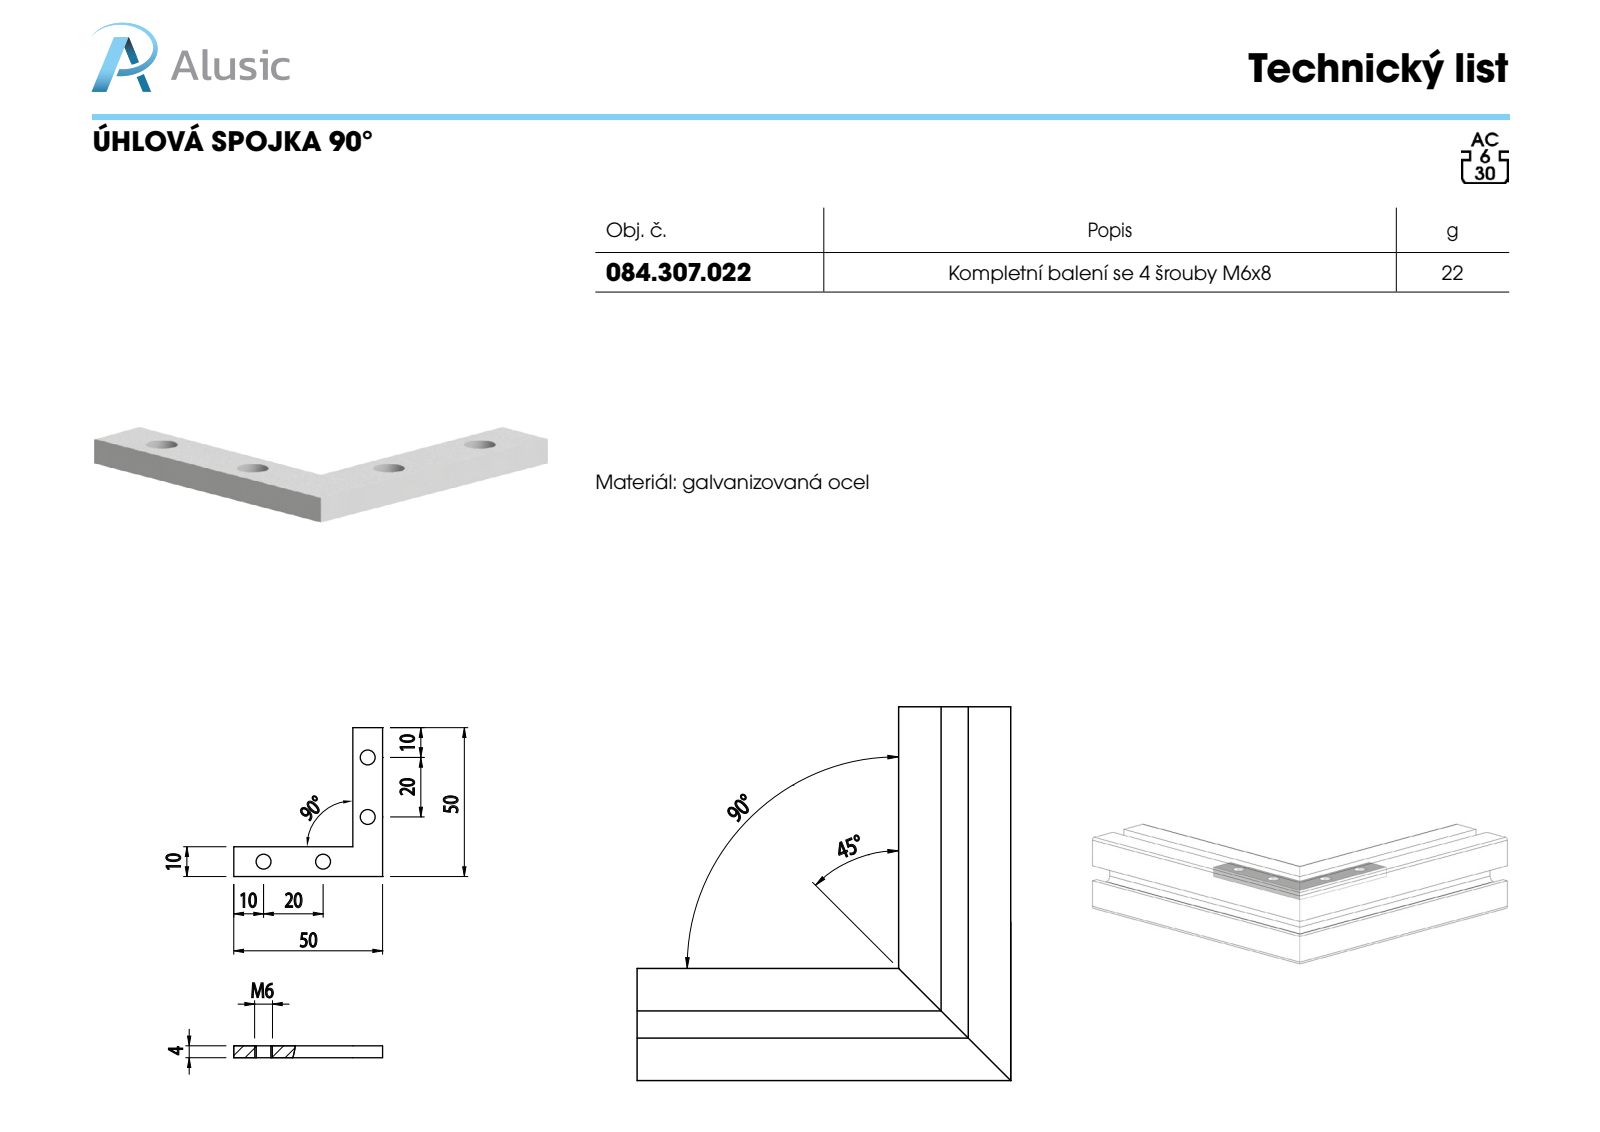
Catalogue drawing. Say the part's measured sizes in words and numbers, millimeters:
The part is named "084.307.022". Its 3-D file was written by "SolidWorks 2011 (CONFIG_CONTROL_DESIGN)". It is 1 solid with 16 faces: 8 planar, 8 cylindrical and 0 other. Overall it measures 50 by 50 by 4 millimeters. Its volume is 3 286 cubic millimeters and its surface area 2 694 square millimeters. Round holes: 4 of diameter 5. The main face-to-face distances are 4, 10, 40, 50. The hole center spacings are 20, 38.08, 21.21, 49.5.
